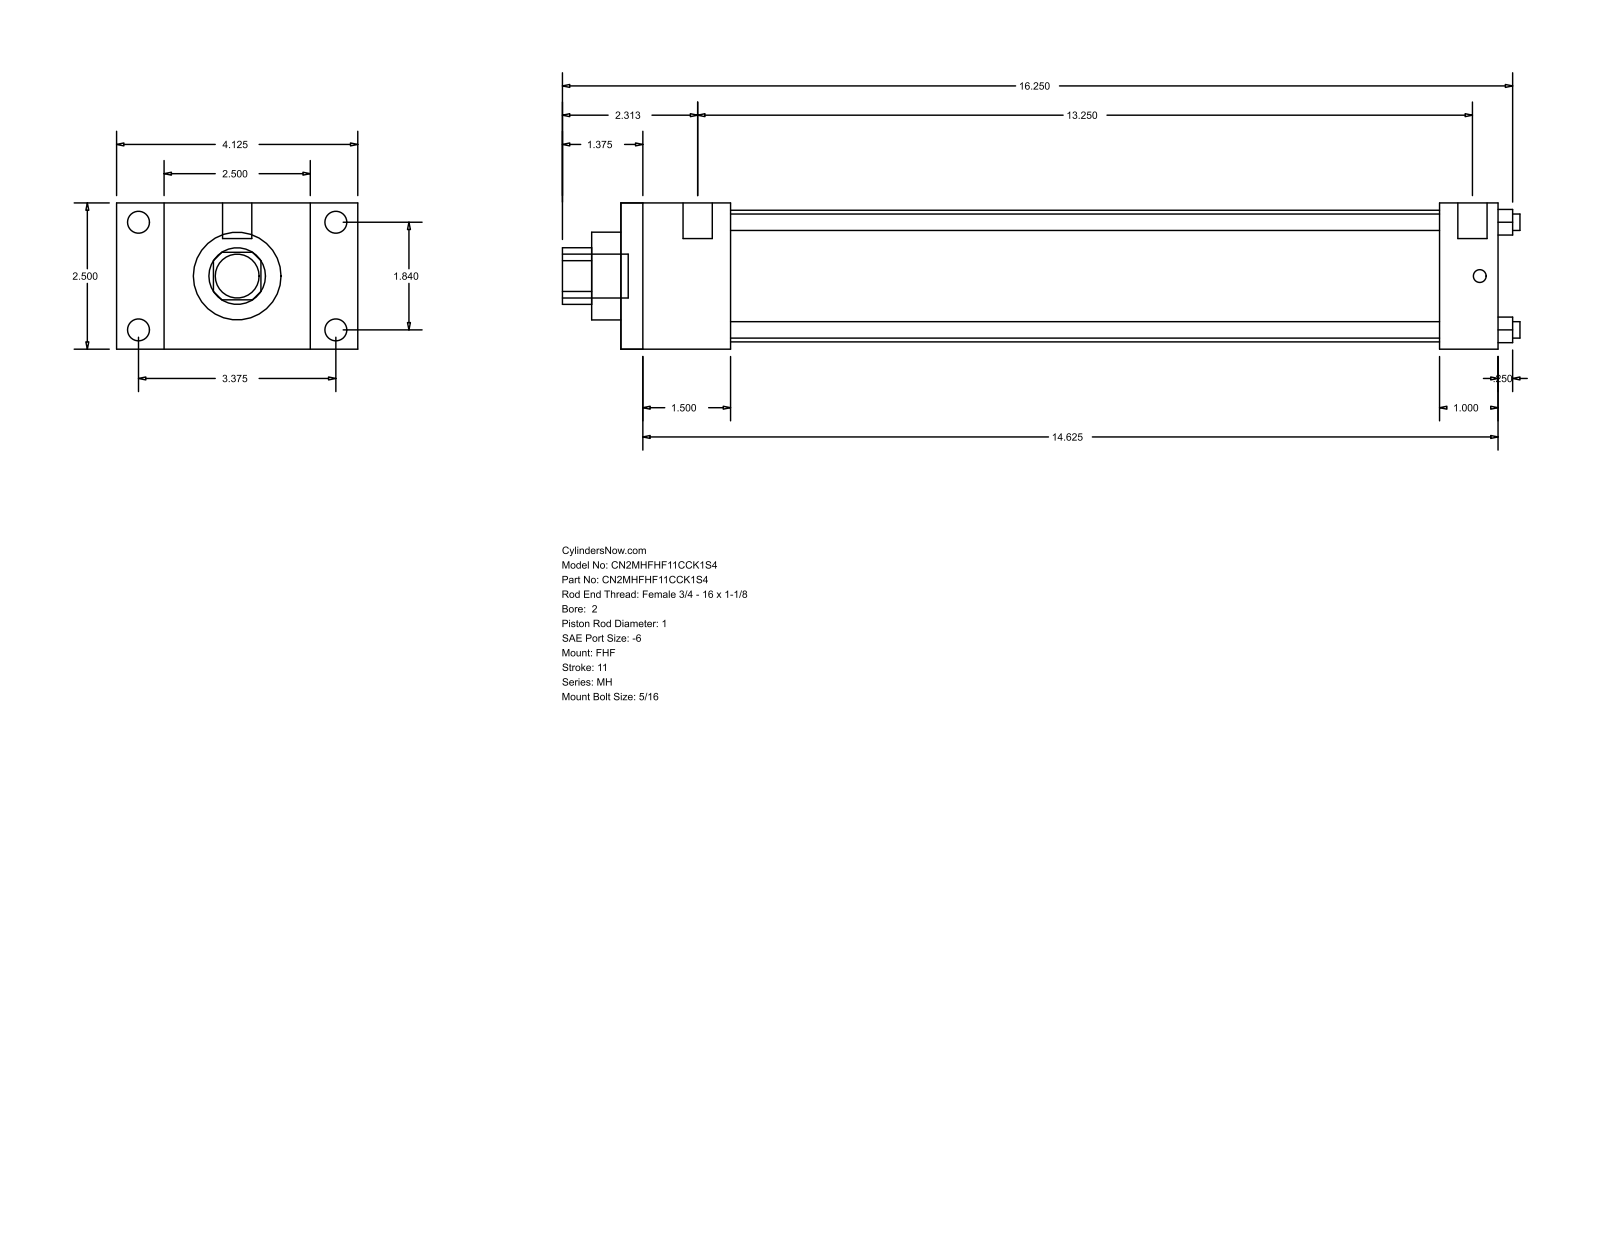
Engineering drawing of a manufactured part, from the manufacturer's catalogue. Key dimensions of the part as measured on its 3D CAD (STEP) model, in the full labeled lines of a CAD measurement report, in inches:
Part name (STEP PRODUCT): MH_FHF__0200_1
STEP written by: GSSL Pune (CONFIG_CONTROL_DESIGN)
Units: inches
Bodies: 0 solids, 88 faces (60 planar, 28 cylindrical, 0 other)
Overall size (bounding box): 16.375 × 4.125 × 2.5
Round holes (diameter × count): ⌀0.281 ×4, ⌀1 ×1, ⌀1.5 ×1, ⌀2.25 ×1
Round bosses / shafts (diameter × count): ⌀0.375 ×4, ⌀0.219 ×4, ⌀0.5 ×2, ⌀0.75 ×1
Partial cylindrical surfaces — rounded edges, fillets, slot ends (radius × count): R0.484 ×1
Main face-to-face distances: 2.5, 15, 1.875, 13.125, 0.813, 3.313, 4.125, 1, 14, 12.125
Hole centre spacings: 1.301, 1.84, 2.602
